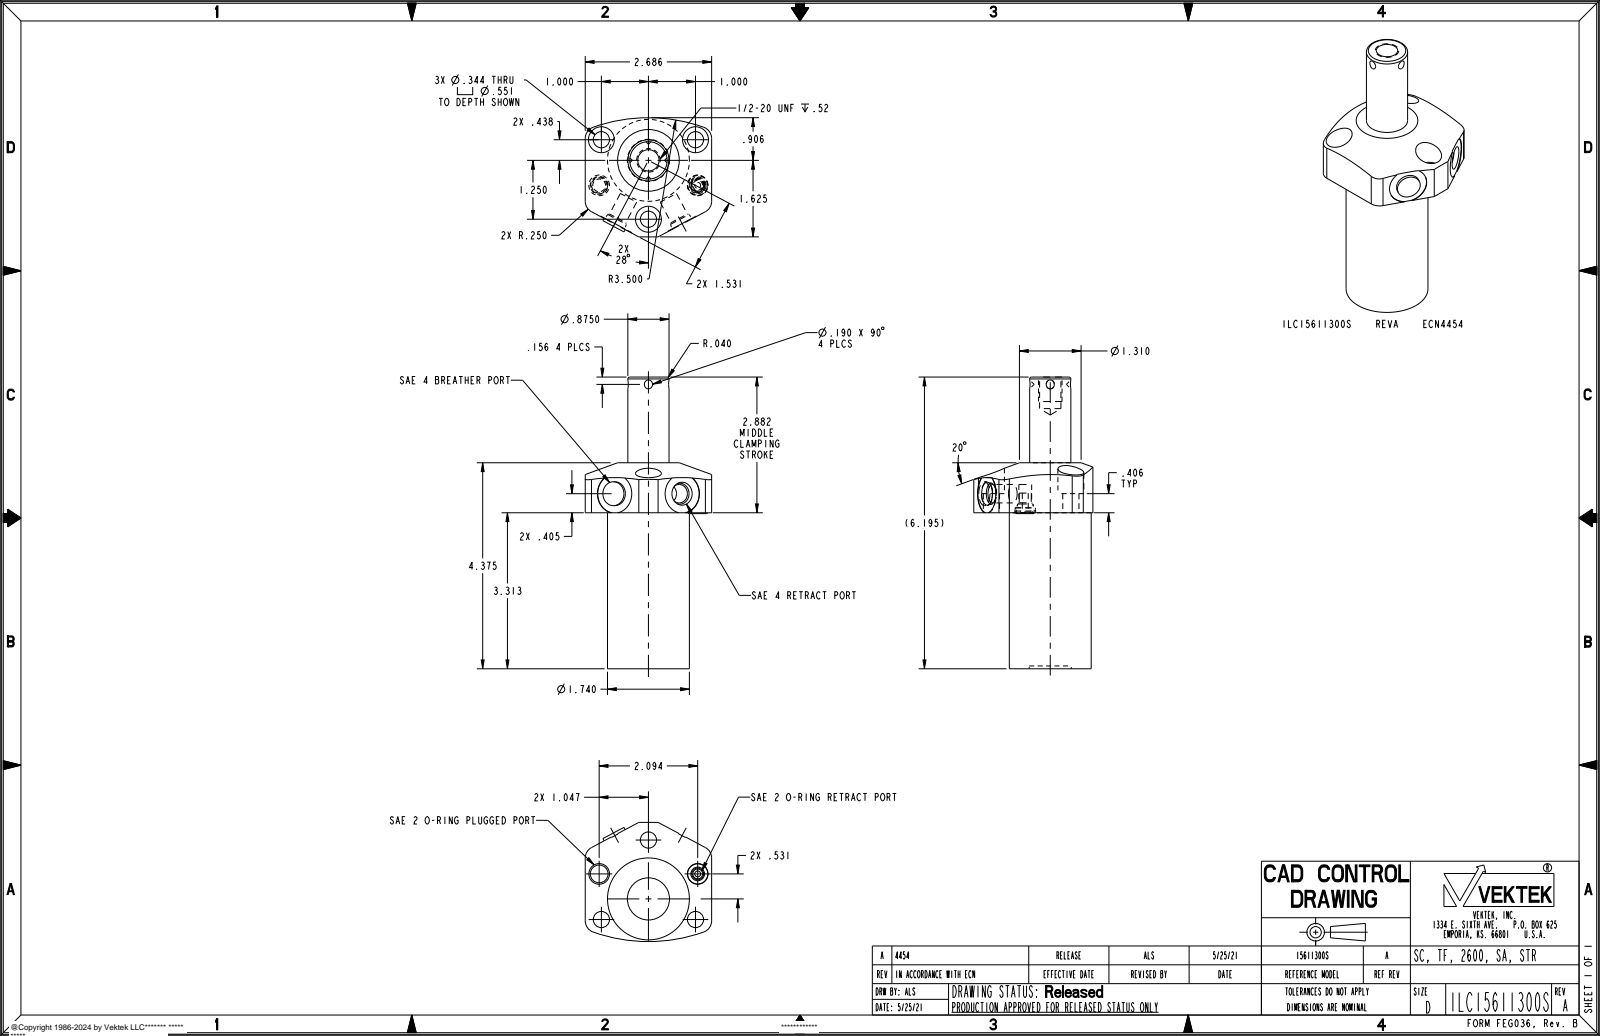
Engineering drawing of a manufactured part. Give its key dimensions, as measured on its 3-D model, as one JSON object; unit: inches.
{"part_name": "ILC15611300S", "step_written_by": "PRO/ENGINEER BY PARAMETRIC TECHNOLOGY CORPORATION, 2013320 (CONFIG_CONTROL_DESIGN)", "units": "inches", "bodies": {"solids": 1, "faces": 122, "planar": 33, "cylindrical": 55, "other": 34}, "overall_size": [6.195, 2.686, 2.531], "volume_in3": 13.63, "surface_area_in2": 51.6, "round_holes": [[0.344, 3], [0.551, 3], [0.272, 2], [0.392, 2], [0.438, 2], [0.125, 1], [0.453, 1], [0.895, 1]], "round_bosses_or_shafts": [[1.74, 1], [0.875, 1], [0.507, 1], [0.5, 1], [0.43, 1], [0.378, 1], [0.256, 1], [0.21, 1]], "partial_cylinders_radius": [[0.25, 4], [0.412, 2], [3.5, 1]], "face_to_face_distances": [3.313, 2.686, 4.375, 1.062, 0.06, 3.253, 4.315, 3.719, 3.659, 0.406], "hole_center_spacings": [0.97, 1.092, 1.174, 1.27, 1.962, 2.265, 1.25, 2]}
